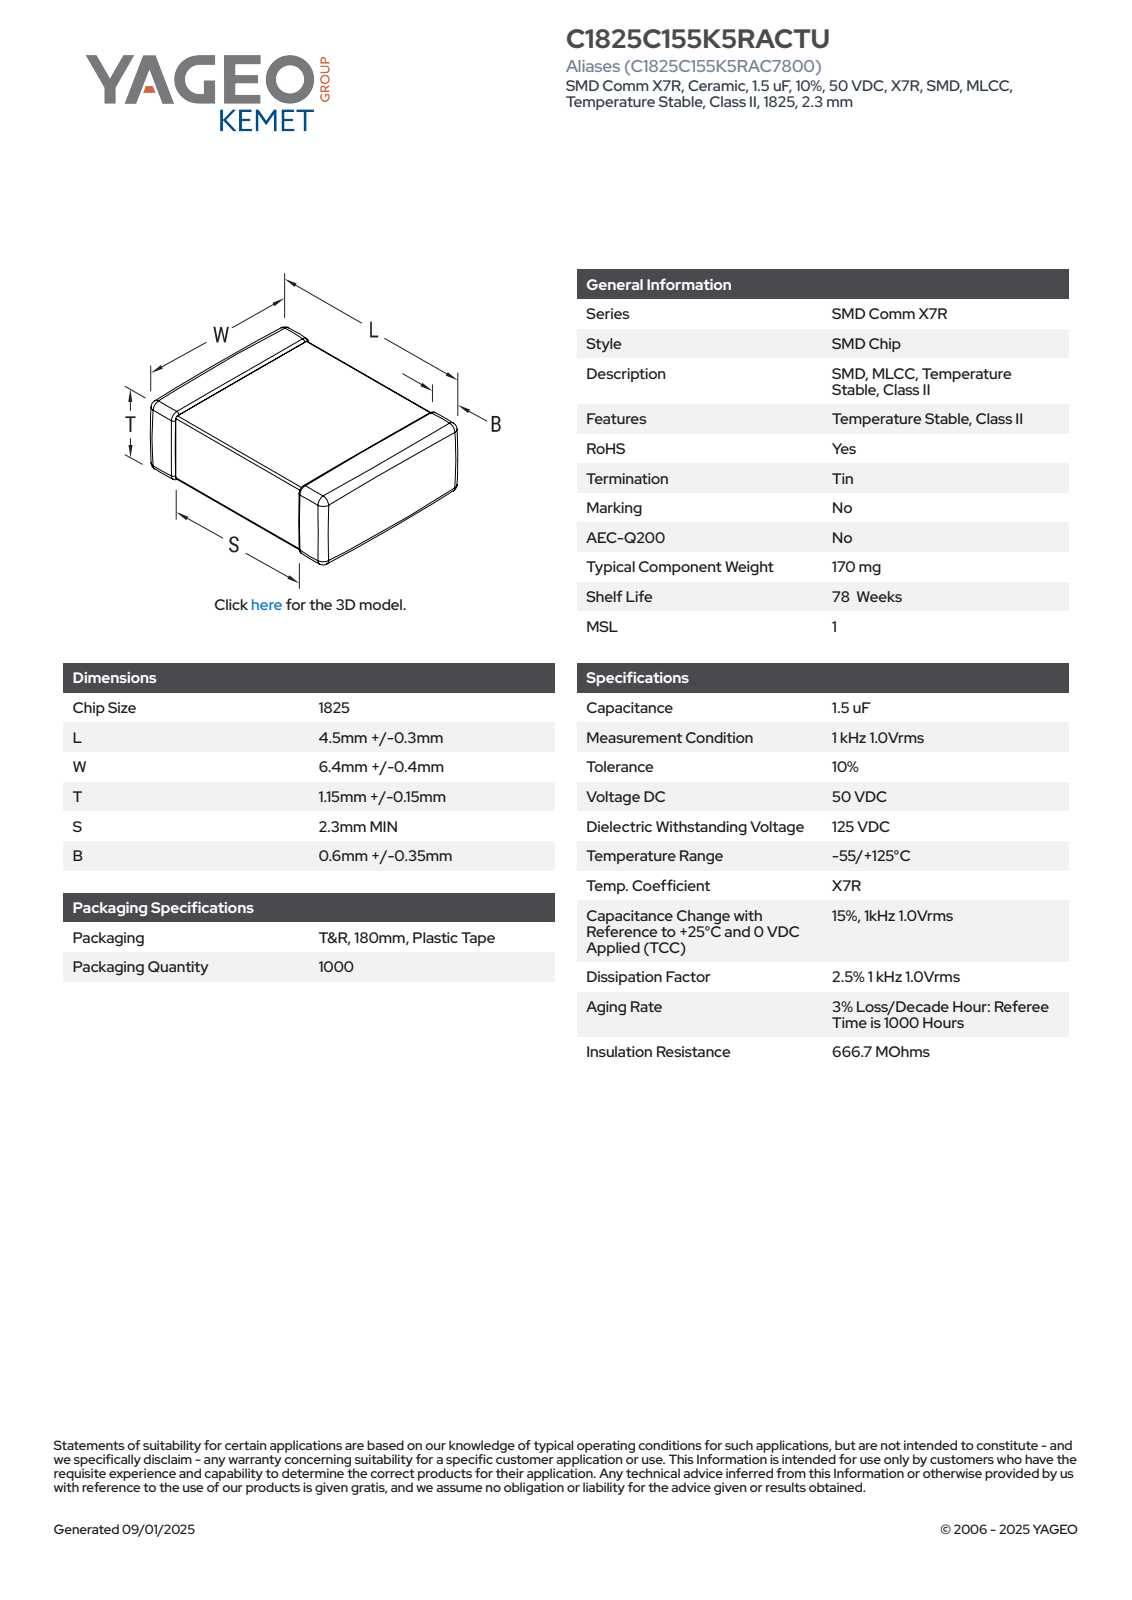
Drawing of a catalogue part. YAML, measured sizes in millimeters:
part_name: "CCS_CCSTD_1825_L4.8W6.8T1.3B0.6"
step_written_by: "SolidWorks 2021 (AUTOMOTIVE_DESIGN)"
units: millimeters
bodies: {solids: 4, faces: 125, planar: 71, cylindrical: 38, other: 16}
overall_size: [6.8, 4.8, 1.3]
volume: 36
surface_area: 98
partial_cylinders:
  - {radius: 0.14, count: 24}
face_to_face_distances: [1.02, 1.16, 1.3, 4.8, 6.66, 6.52, 6.8, 1.59, 3.21, 2.59]
